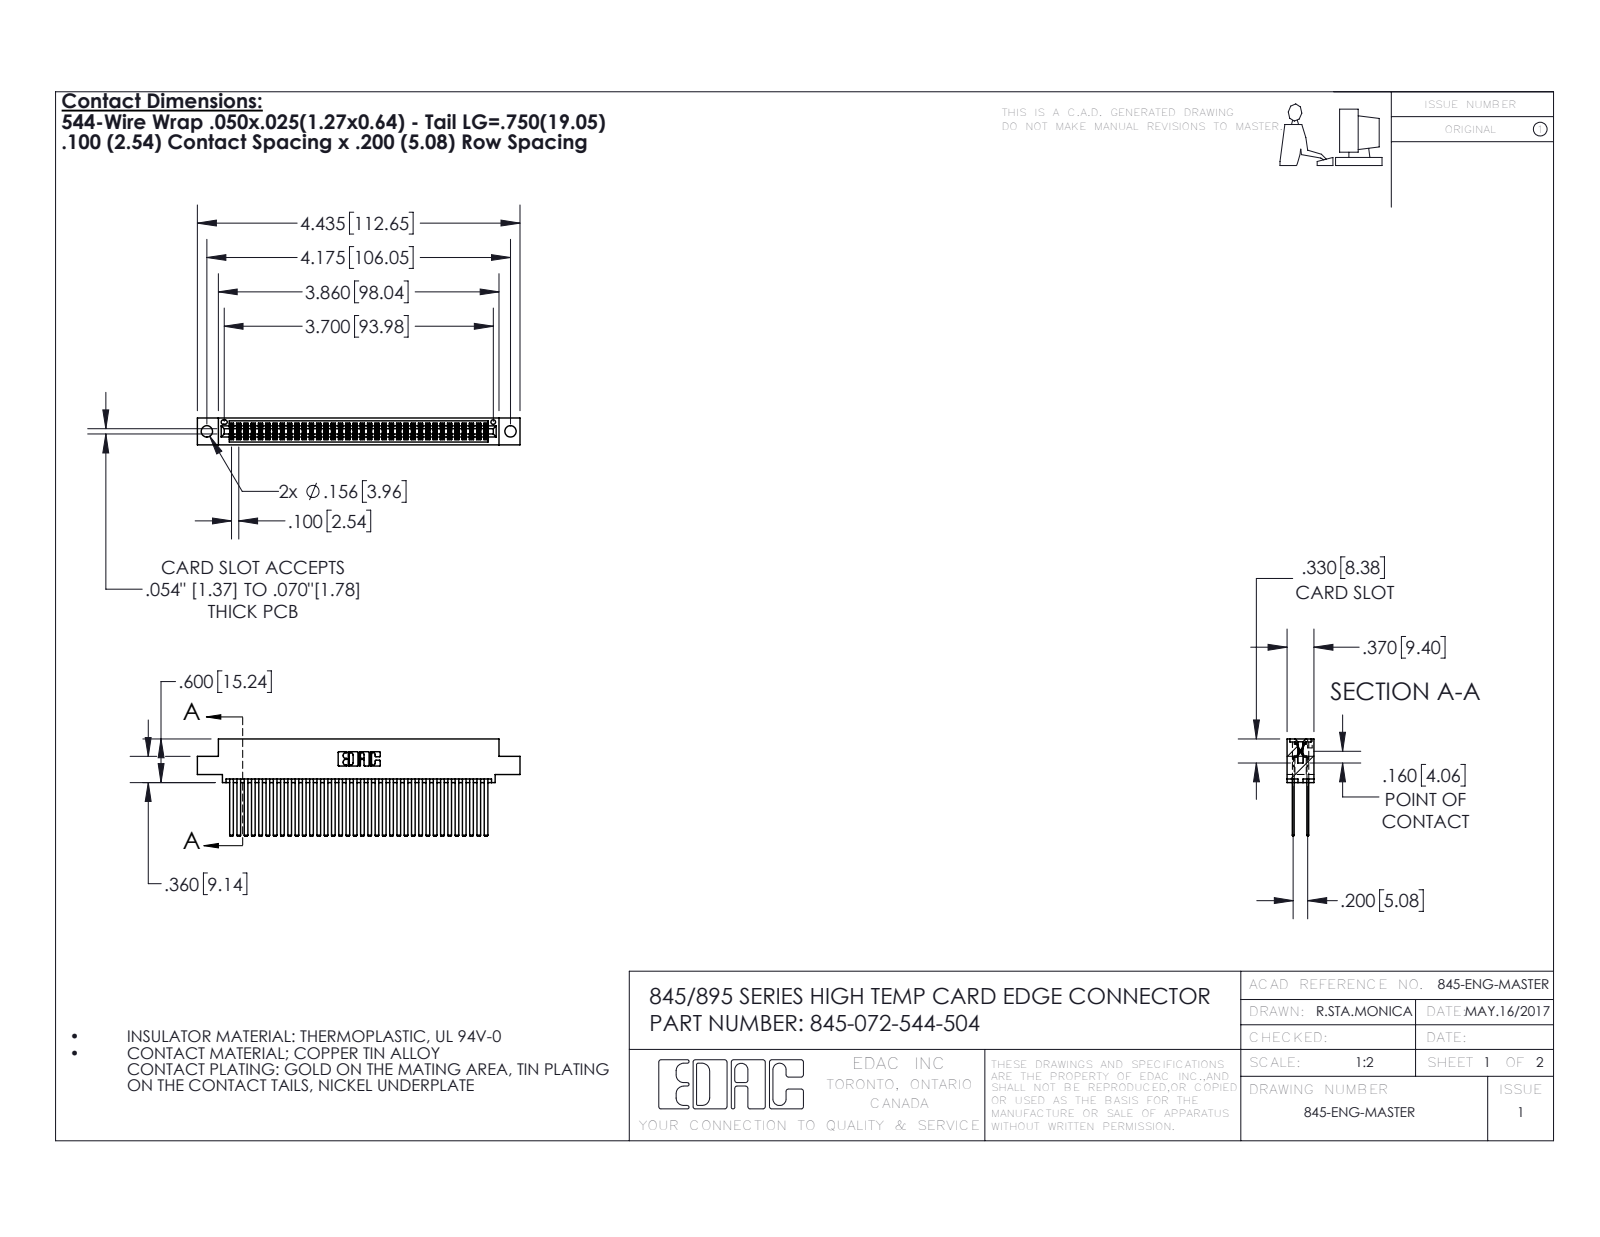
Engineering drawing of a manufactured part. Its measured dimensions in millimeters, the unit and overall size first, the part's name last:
Units: millimetres
Overall size (bounding box): 112.6 × 34 × 9.4
Round holes (diameter × count): ⌀4 ×2, ⌀1.6 ×1
Partial cylindrical surfaces — rounded edges, fillets, slot ends (radius × count): R0.2 ×108, R0.3 ×22, R0.2 ×6, R0.8 ×6, R0.7 ×3, R0.4 ×2, R0.5 ×2, R0.6 ×2
Main face-to-face distances: 5.1, 0.6, 7.6, 1.8, 2.5, 6.9, 5.7, 4.4, 9.4, 1.3
Hole centre spacings: 6.9, 100.1, 106
Volume: 11 700 mm³ · Surface area: 20 100 mm²
Bodies: 73 solids, 3298 faces (2172 planar, 1126 cylindrical, 0 other)
Part name (STEP PRODUCT): 345-072-544-504; 345 Part_0.110 Offset - 0.156 Dia-TH; 345-292-001_345-293-144
STEP written by: SolidWorks 2016 (CONFIG_CONTROL_DESIGN)
